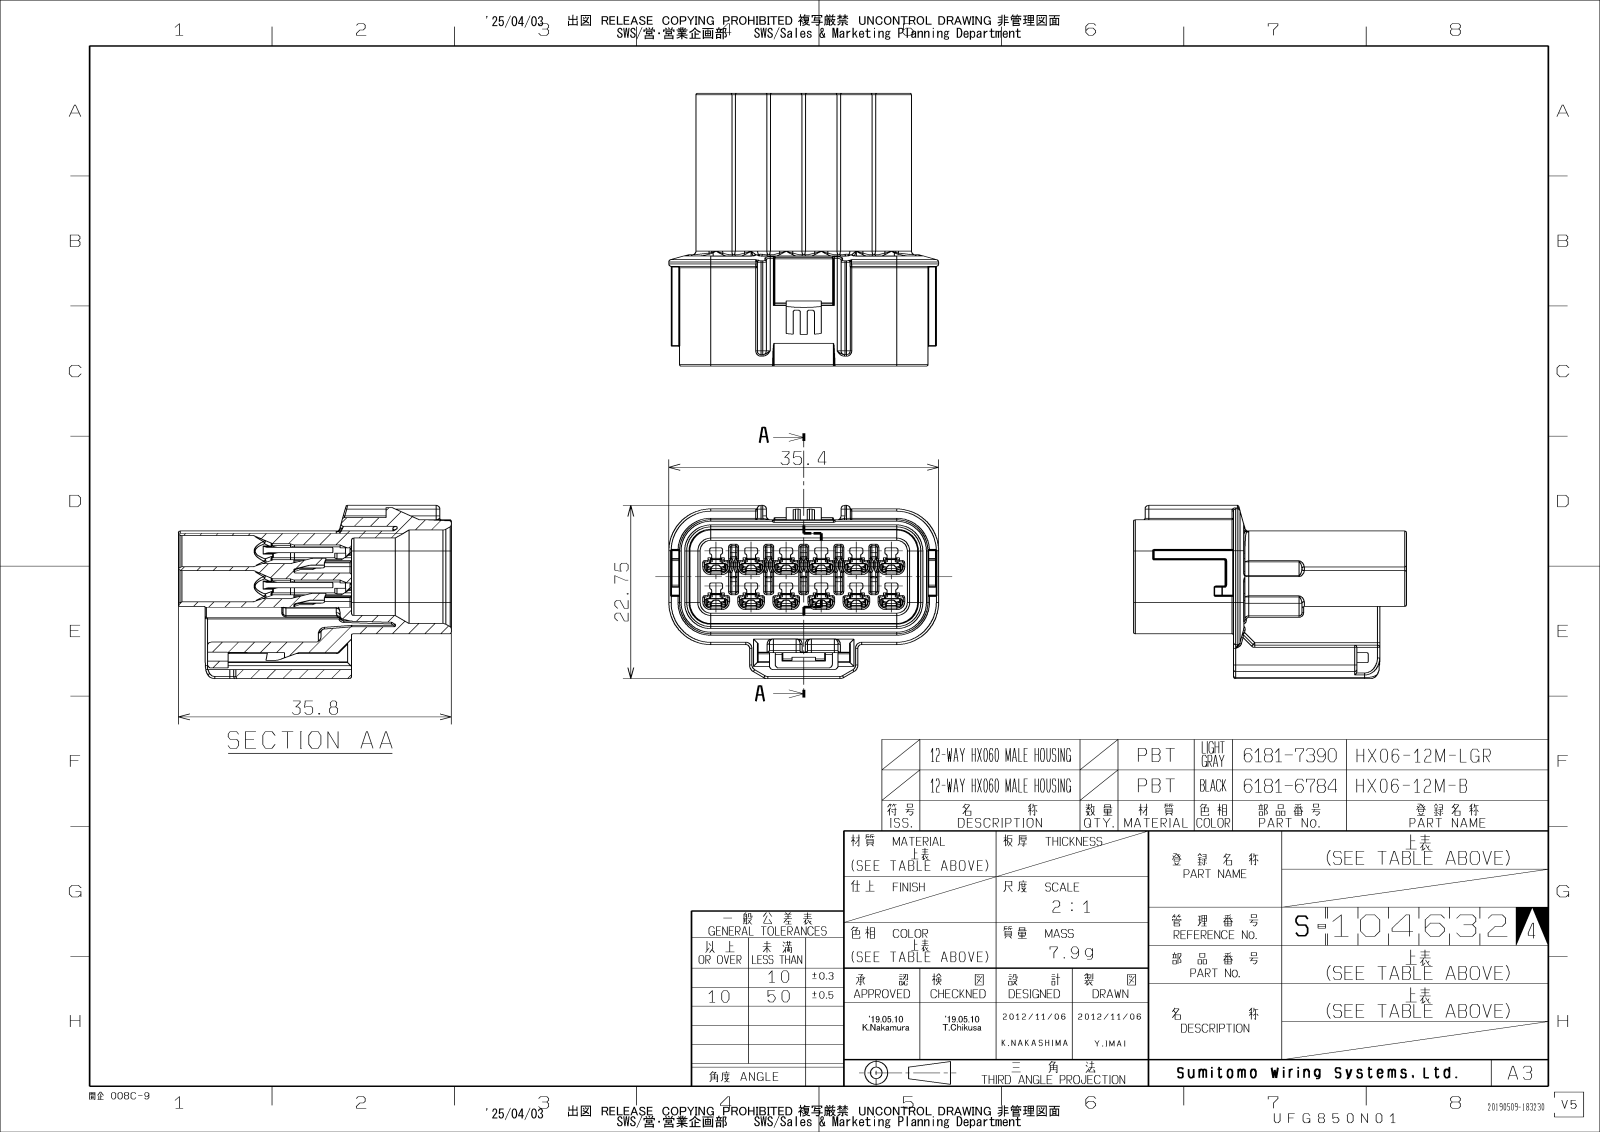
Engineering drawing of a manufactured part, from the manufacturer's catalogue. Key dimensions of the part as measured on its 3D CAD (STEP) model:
Part name (STEP PRODUCT): 6181-6784
STEP written by: CATIA V5 STEP AP214 v2 (AUTOMOTIVE_DESIGN)
Units: millimetres
Bodies: 1 solid, 323 faces (241 planar, 67 cylindrical, 15 other)
Overall size (bounding box): 35.8 × 35.4 × 22.75
Volume: 9 382 mm³ · Surface area: 7 063 mm²
Round holes (diameter × count): ⌀4.1 ×12
Partial cylindrical surfaces — rounded edges, fillets, slot ends (radius × count): R2.65 ×12, R1 ×4, R1.7 ×4, R2.75 ×4, R4.1 ×4, R5.5 ×4, R1.65 ×2, R2 ×1
Main face-to-face distances: 2.4, 12.55, 1.35, 1.05, 11.2, 0.8, 1, 14.95, 9, 13.6
Hole centre spacings: 4.6, 6.51, 9.2, 10.29, 13.8, 14.55, 18.4, 18.97
